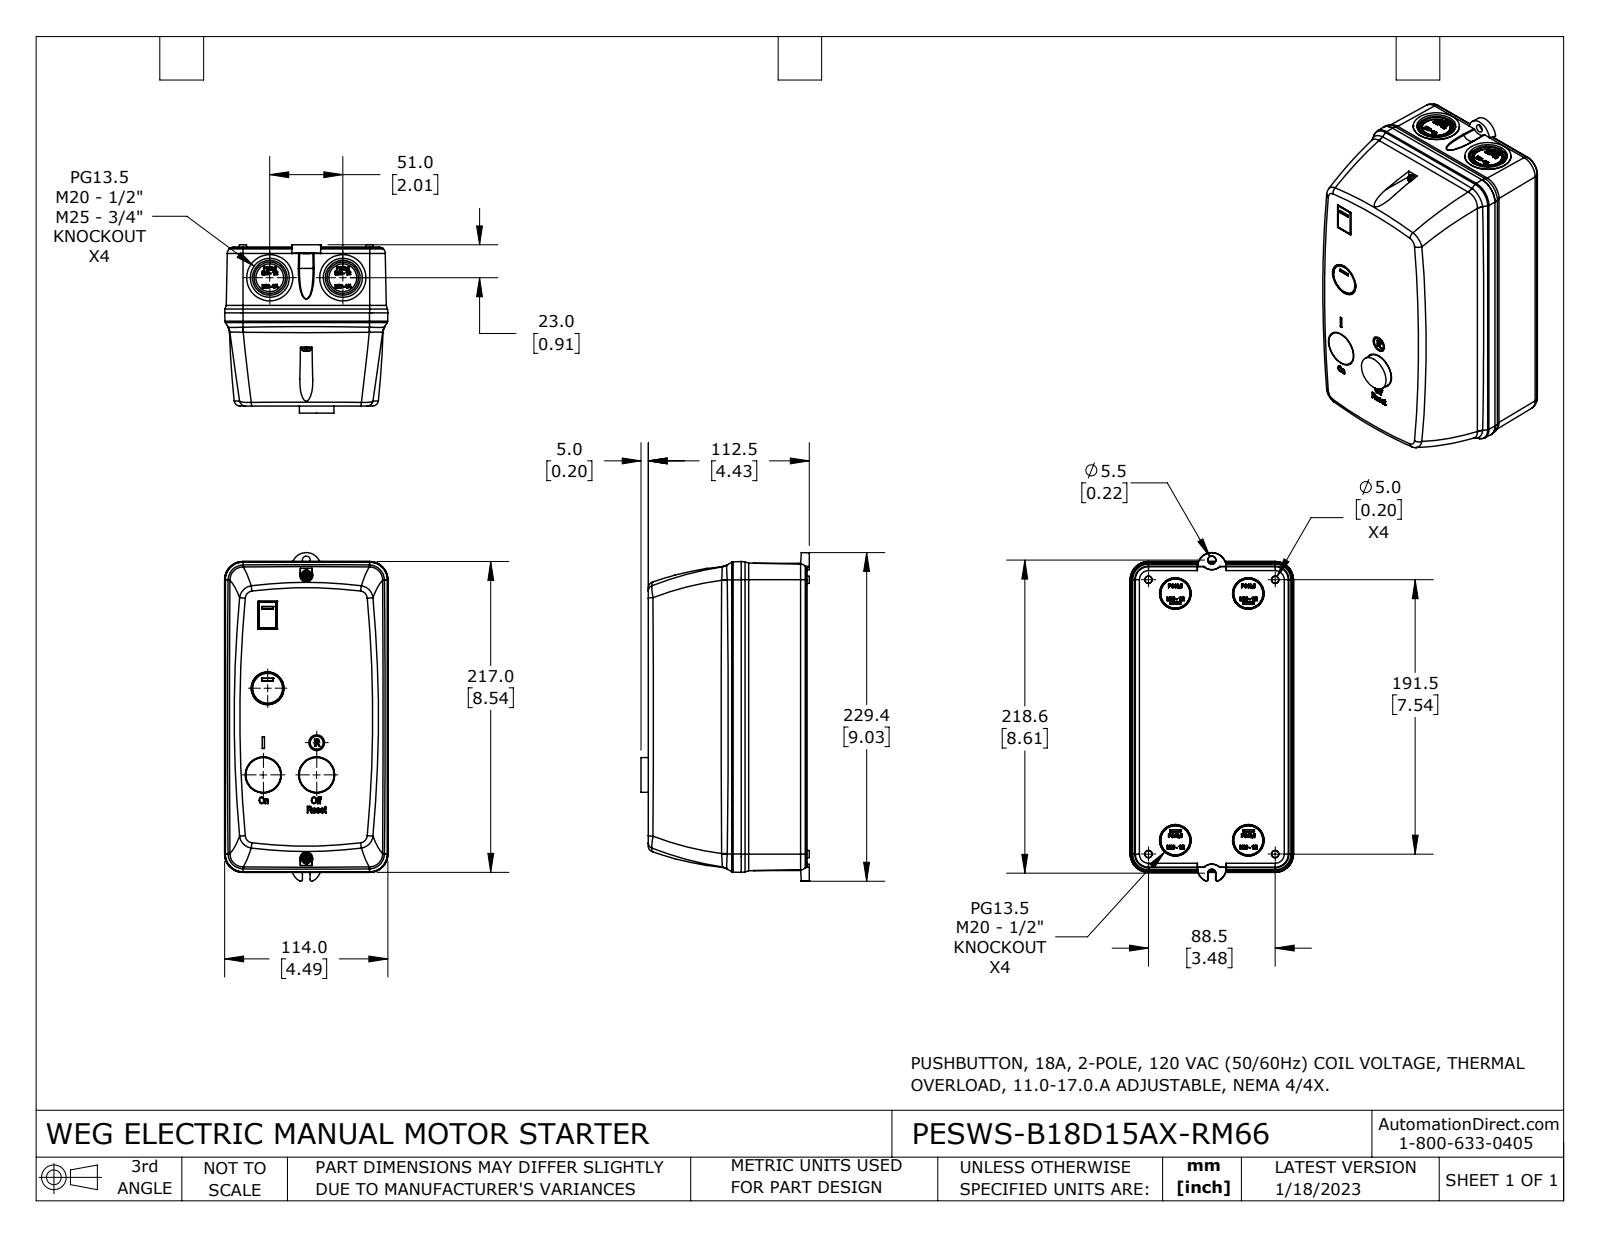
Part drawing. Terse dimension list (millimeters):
name: PESWS-B18D15AX-RM66
written by: SolidWorks 2021 (CONFIG_CONTROL_DESIGN)
unit: mm
bodies: 6 solids, 2195 faces (1110 planar, 92 cylindrical, 993 other)
size: 229.44 × 117.5 × 114.01
volume: 2 457 000 mm³; area: 166 196 mm²
holes: 2× ⌀4.4, 2× ⌀21.91, 2× ⌀27.24, 1× ⌀5.5, 1× ⌀11
bosses: 2× ⌀32.26, 2× ⌀24.25, 2× ⌀24.2, 2× ⌀19.37, 2× ⌀7, 2× ⌀3, 1× ⌀9
rounds: 4× R2, 4× R4.61, 4× R9.54, 2× R6.54, 2× R7.54, 1× R2.08, 1× R2.17, 1× R2.75
face distances: 46, 65, 111, 0.5, 110.5, 45.5, 110, 1, 109.5, 64
hole spacings: 10.5, 51, 81.32, 117.22, 127.71, 198, 208.5
